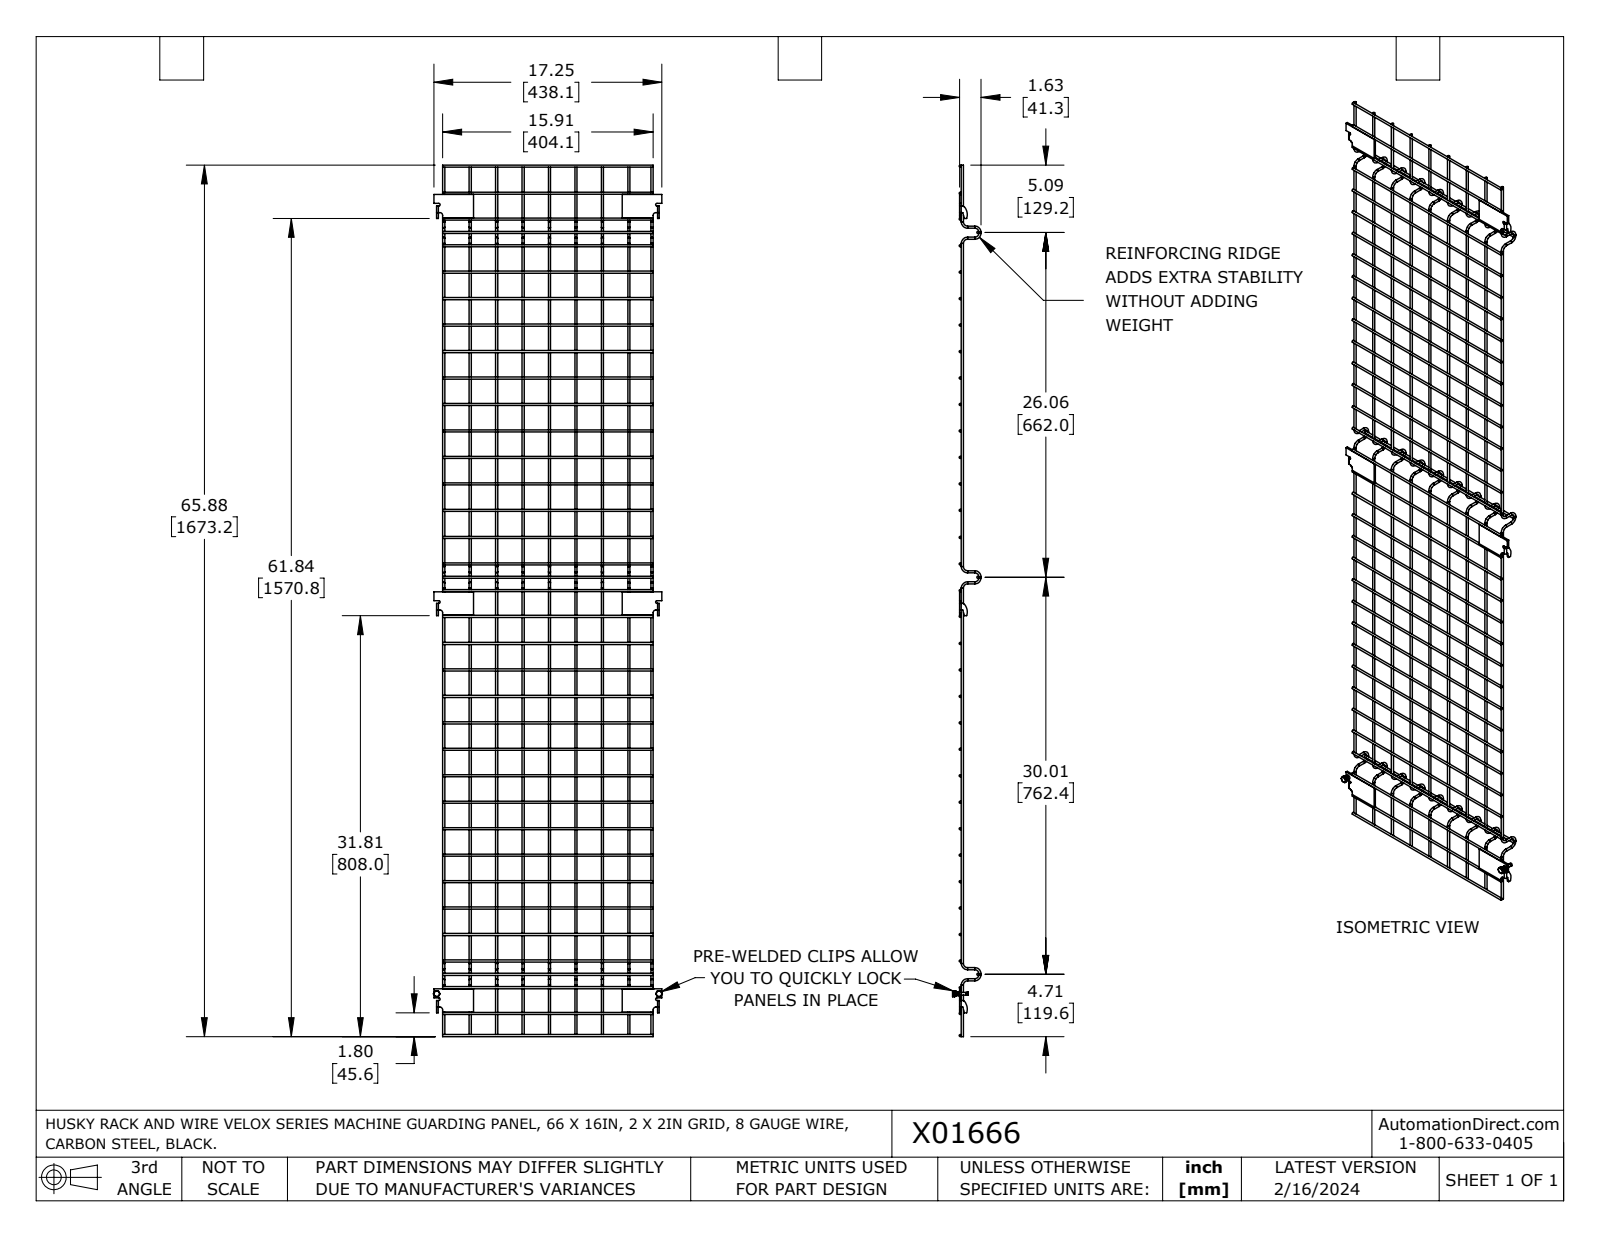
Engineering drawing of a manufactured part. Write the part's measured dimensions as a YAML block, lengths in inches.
part_name: "X01666"
step_written_by: "SolidWorks 2023 (AUTOMOTIVE_DESIGN)"
units: inches
bodies: {solids: 56, faces: 534, planar: 200, cylindrical: 202, other: 132}
overall_size: [65.875, 17.313, 2.103]
volume: 28.98
surface_area: 696.4
round_holes:
  - {diameter: 0.201, count: 2}
  - {diameter: 0.25, count: 2}
round_bosses_or_shafts:
  - {diameter: 0.16, count: 109}
  - {diameter: 0.39, count: 2}
  - {diameter: 0.245, count: 2}
  - {diameter: 0.187, count: 2}
partial_cylinders:
  - {radius: 0.1, count: 6}
  - {radius: 0.218, count: 6}
  - {radius: 0.25, count: 3}
  - {radius: 0.865, count: 3}
  - {radius: 0.009, count: 2}
  - {radius: 0.067, count: 2}
  - {radius: 0.134, count: 2}
face_to_face_distances: [0.134, 0.125, 1.765, 30.031, 0.467, 16.377, 30.016, 60.047, 2.798, 14.046]
hole_center_spacings: [16.808]
